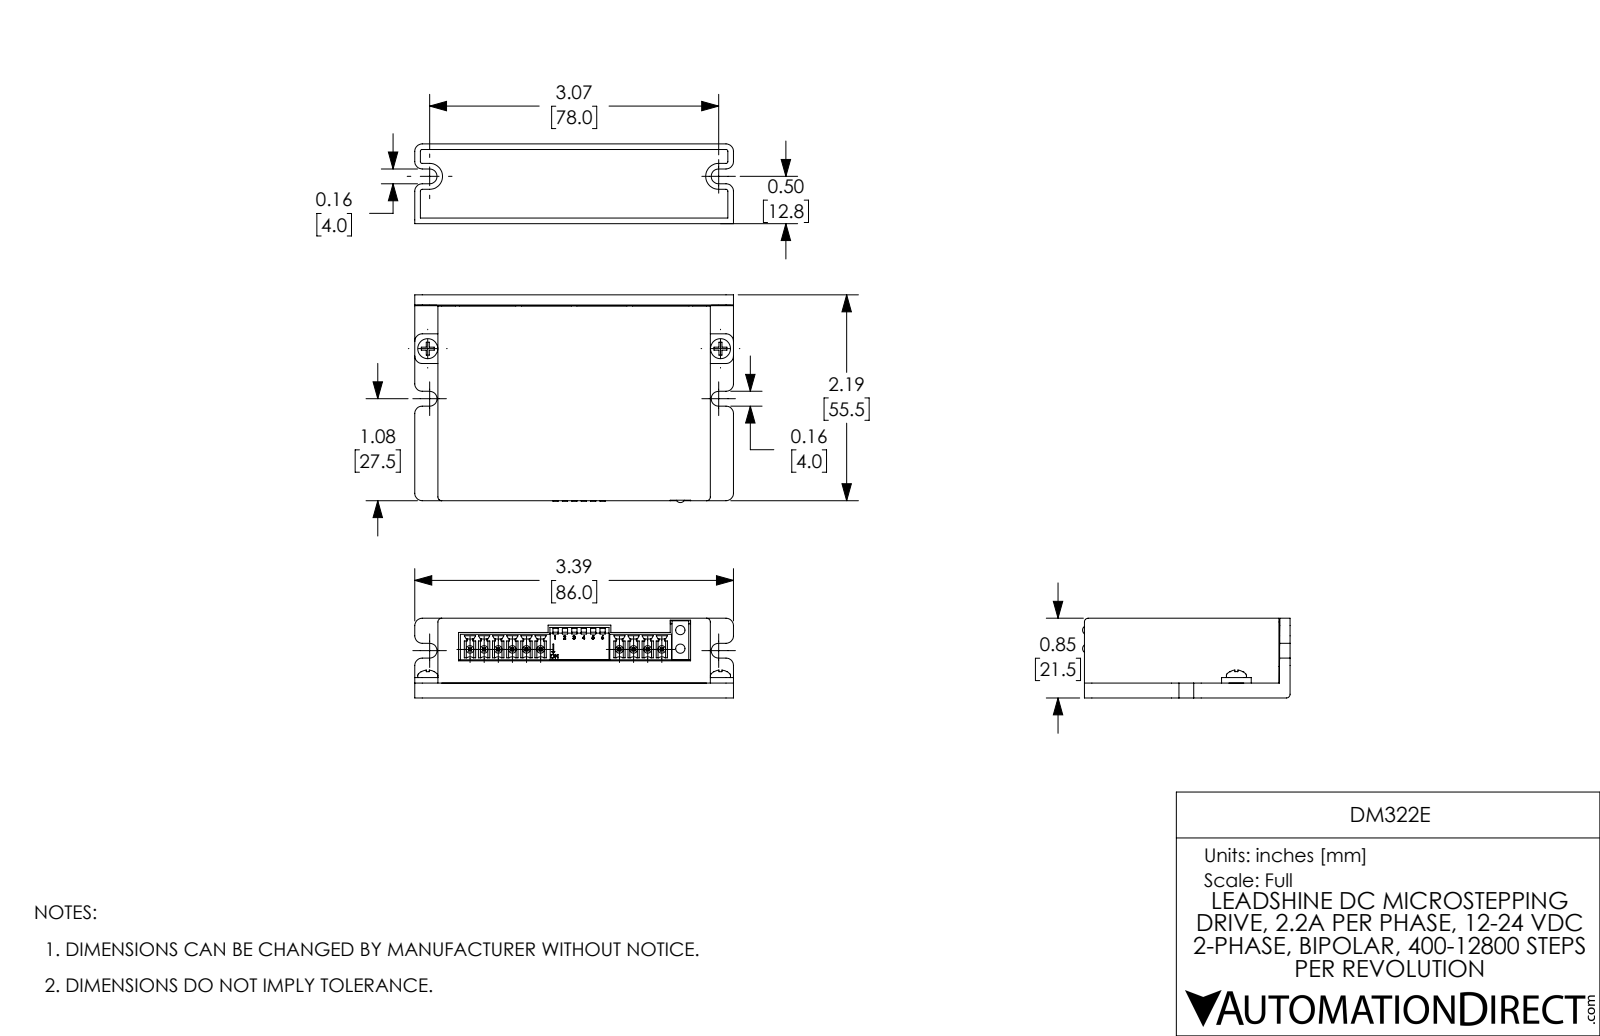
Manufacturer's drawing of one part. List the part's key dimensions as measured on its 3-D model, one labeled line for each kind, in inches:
Part name (STEP PRODUCT): DM322E_3D
STEP written by: SolidWorks 2017 (AUTOMOTIVE_DESIGN)
Units: inches
Bodies: 9 solids, 1044 faces (805 planar, 159 cylindrical, 80 other)
Overall size (bounding box): 3.386 × 2.205 × 0.846
Volume: 2.096 in³ · Surface area: 63.22 in²
Round holes (diameter × count): ⌀0.098 ×6, ⌀0.138 ×6
Round bosses / shafts (diameter × count): ⌀0.08 ×10, ⌀0.228 ×4, ⌀0.213 ×2, ⌀0.118 ×2, ⌀0.098 ×2, ⌀0.016 ×2
Partial cylindrical surfaces — rounded edges, fillets, slot ends (radius × count): R0.079 ×20, R0.02 ×12, R0.06 ×10, R0.039 ×6, R0.138 ×4, R0.114 ×2, R0.022 ×1
Main face-to-face distances: 0.059, 0.098, 0.787, 0.441, 0.689, 0.248, 0.346, 0.382, 0.63, 0.283
Hole centre spacings: 0.382, 1.165, 1.339, 2.48, 2.804, 2.819, 3.012, 3.11
